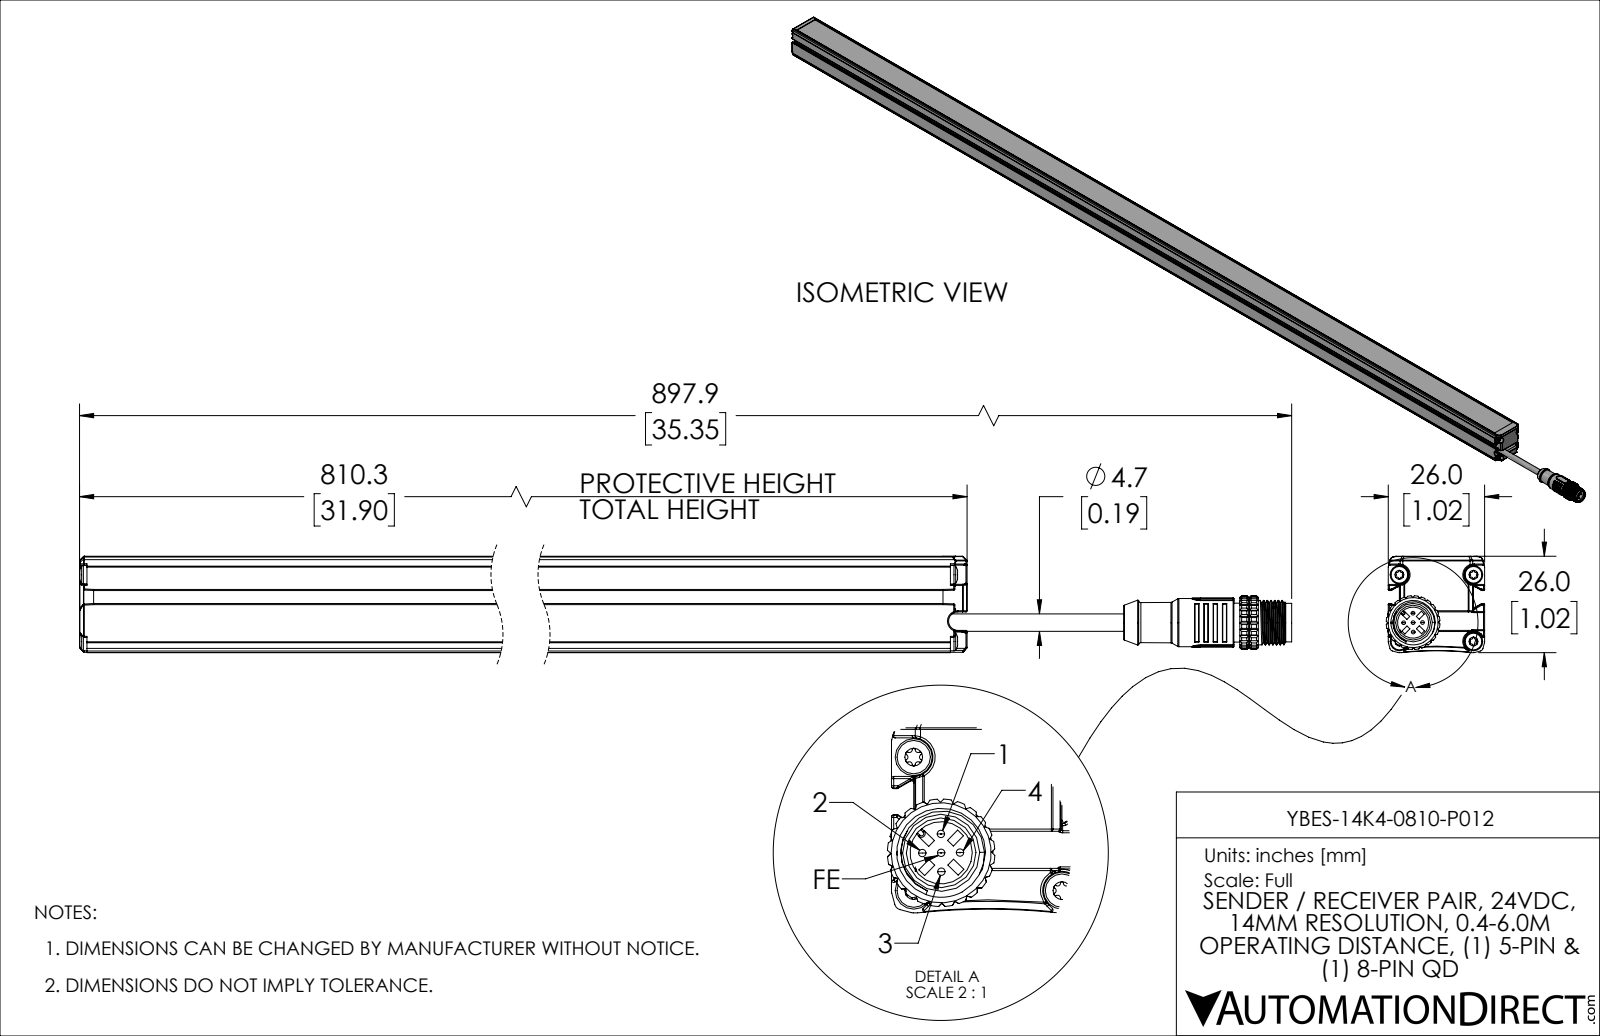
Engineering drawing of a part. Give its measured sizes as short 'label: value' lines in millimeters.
name: YBES-14K4-0810-P012_REV1
written by: SolidWorks 2019 (AUTOMOTIVE_DESIGN)
unit: mm
bodies: 2 solids, 1741 faces (547 planar, 719 cylindrical, 475 other)
size: 897.9 × 26.5 × 26
volume: 191 200 mm³; area: 208 300 mm²
holes: 4× ⌀2.4, 4× ⌀2.5, 4× ⌀3.7, 4× ⌀5, 1× ⌀4.8, 1× ⌀5.9, 1× ⌀8.4
bosses: 5× ⌀1, 4× ⌀3.2, 4× ⌀2.5, 4× ⌀1.3, 2× ⌀1.5, 1× ⌀13.5, 1× ⌀13, 1× ⌀12
rounds: 153× R0.2, 115× R0.3, 24× R0.2, 24× R0.4, 18× R1, 16× R0.4, 10× R0.2, 7× R0.5
face distances: 3, 1.5, 1.8, 21.2, 26, 18.2, 1.2, 0.4, 23, 4.8
hole spacings: 18, 20, 26.9, 6.3, 13.4, 17.1, 20.8
